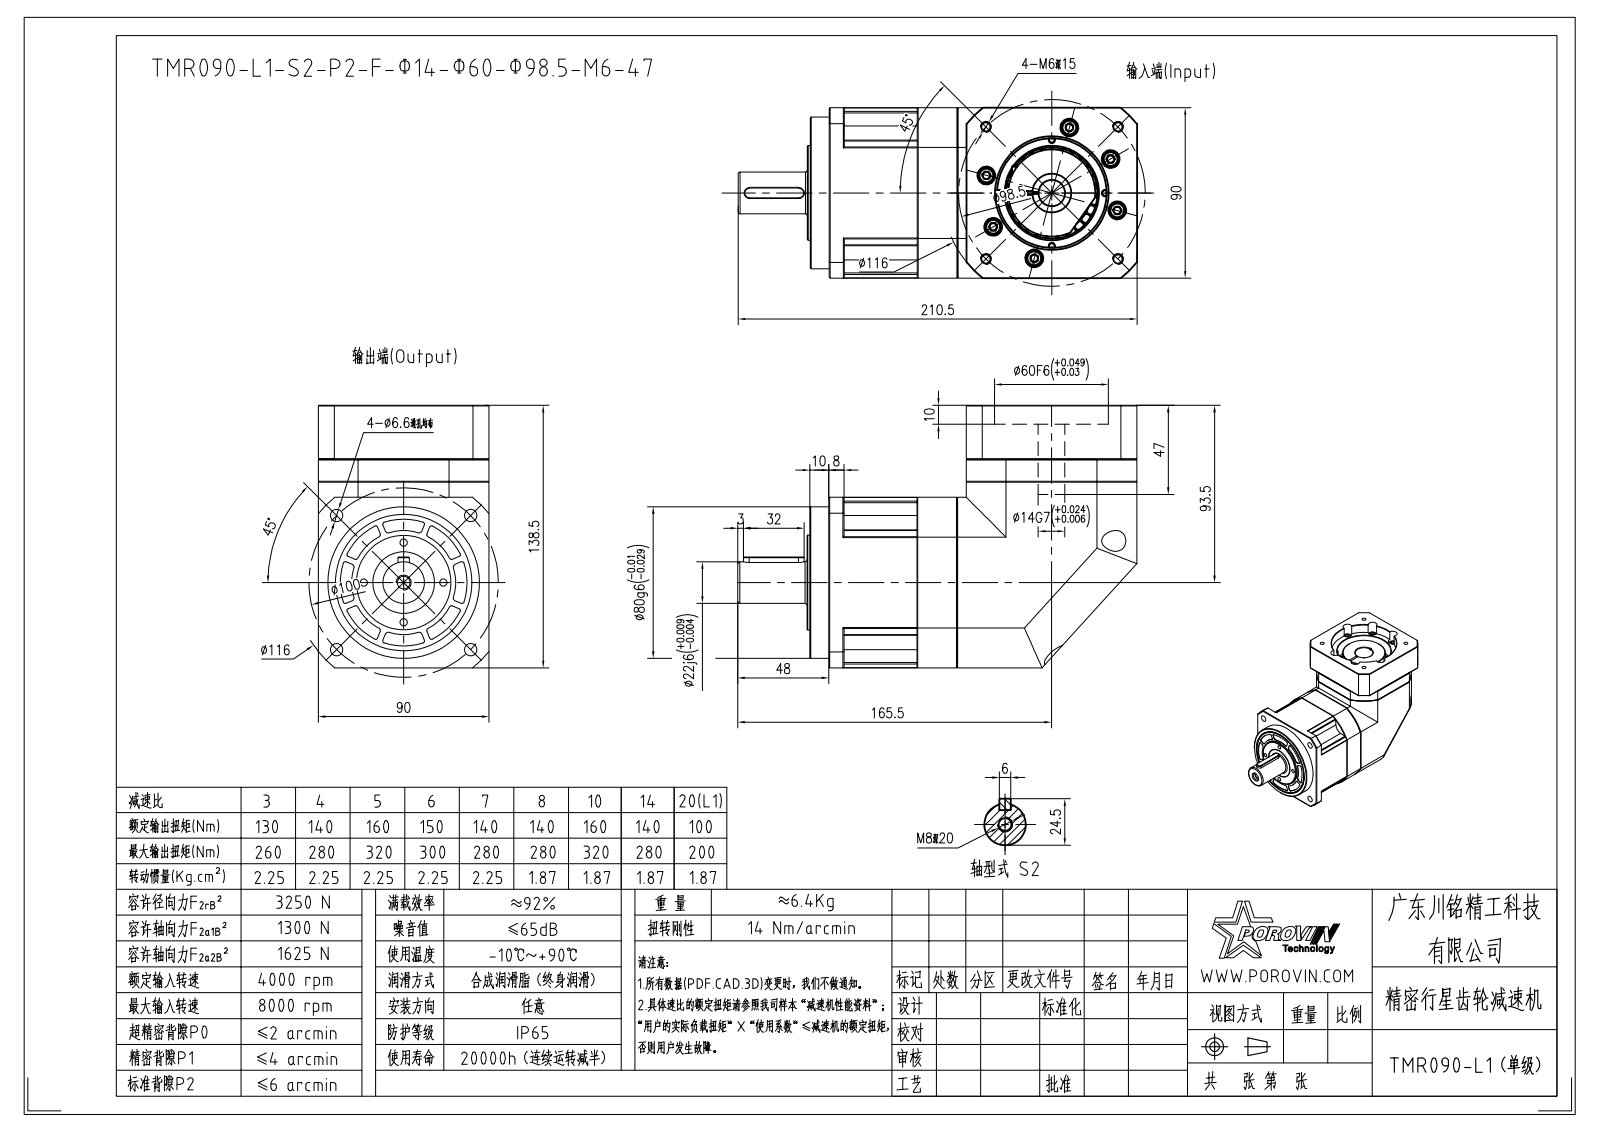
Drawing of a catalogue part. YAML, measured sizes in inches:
part_name: "HEXAGON_SOCKET_HEAD_CAP_S-30720; HEXAGON_SOCKET_HEAD_CAP_SC-9242; HEXAGON_SOCKET_HEAD_CAP_S-20065; SPRING_LOCK_WASHERS--NORM-30785 (+8 more)"
step_written_by: "CREO PARAMETRIC BY PTC INC, 2020053 (CONFIG_CONTROL_DESIGN)"
units: inches
bodies: {solids: 43, faces: 1285, planar: 516, cylindrical: 543, other: 226}
overall_size: [8.287, 5.453, 3.543]
volume: 82.69
surface_area: 331
round_holes:
  - {diameter: 0.213, count: 12}
  - {diameter: 0.217, count: 12}
  - {diameter: 0.374, count: 12}
  - {diameter: 0.165, count: 7}
  - {diameter: 0.197, count: 5}
  - {diameter: 0.256, count: 5}
  - {diameter: 0.157, count: 4}
  - {diameter: 0.26, count: 4}
  - {diameter: 0.263, count: 4}
  - {diameter: 0.433, count: 4}
  - {diameter: 0.268, count: 1}
  - {diameter: 0.331, count: 1}
round_bosses_or_shafts:
  - {diameter: 0.335, count: 12}
  - {diameter: 0.315, count: 12}
  - {diameter: 0.197, count: 12}
  - {diameter: 0.394, count: 4}
  - {diameter: 0.389, count: 4}
  - {diameter: 0.236, count: 4}
  - {diameter: 3.15, count: 1}
  - {diameter: 3.071, count: 1}
partial_cylinders:
  - {radius: 0.039, count: 92}
  - {radius: 0.295, count: 4}
  - {radius: 2.008, count: 3}
  - {radius: 0.118, count: 2}
  - {radius: 2.283, count: 2}
  - {radius: 0.157, count: 1}
  - {radius: 0.207, count: 1}
  - {radius: 1.575, count: 1}
face_to_face_distances: [3.543, 0.472, 0.839, 0.846, 1.024, 1.122, 0.394, 4.331, 0.197, 0.098]
hole_center_spacings: [1.407, 1.077, 1.502, 2.601, 2.619, 2.675, 0.685, 2.081]
